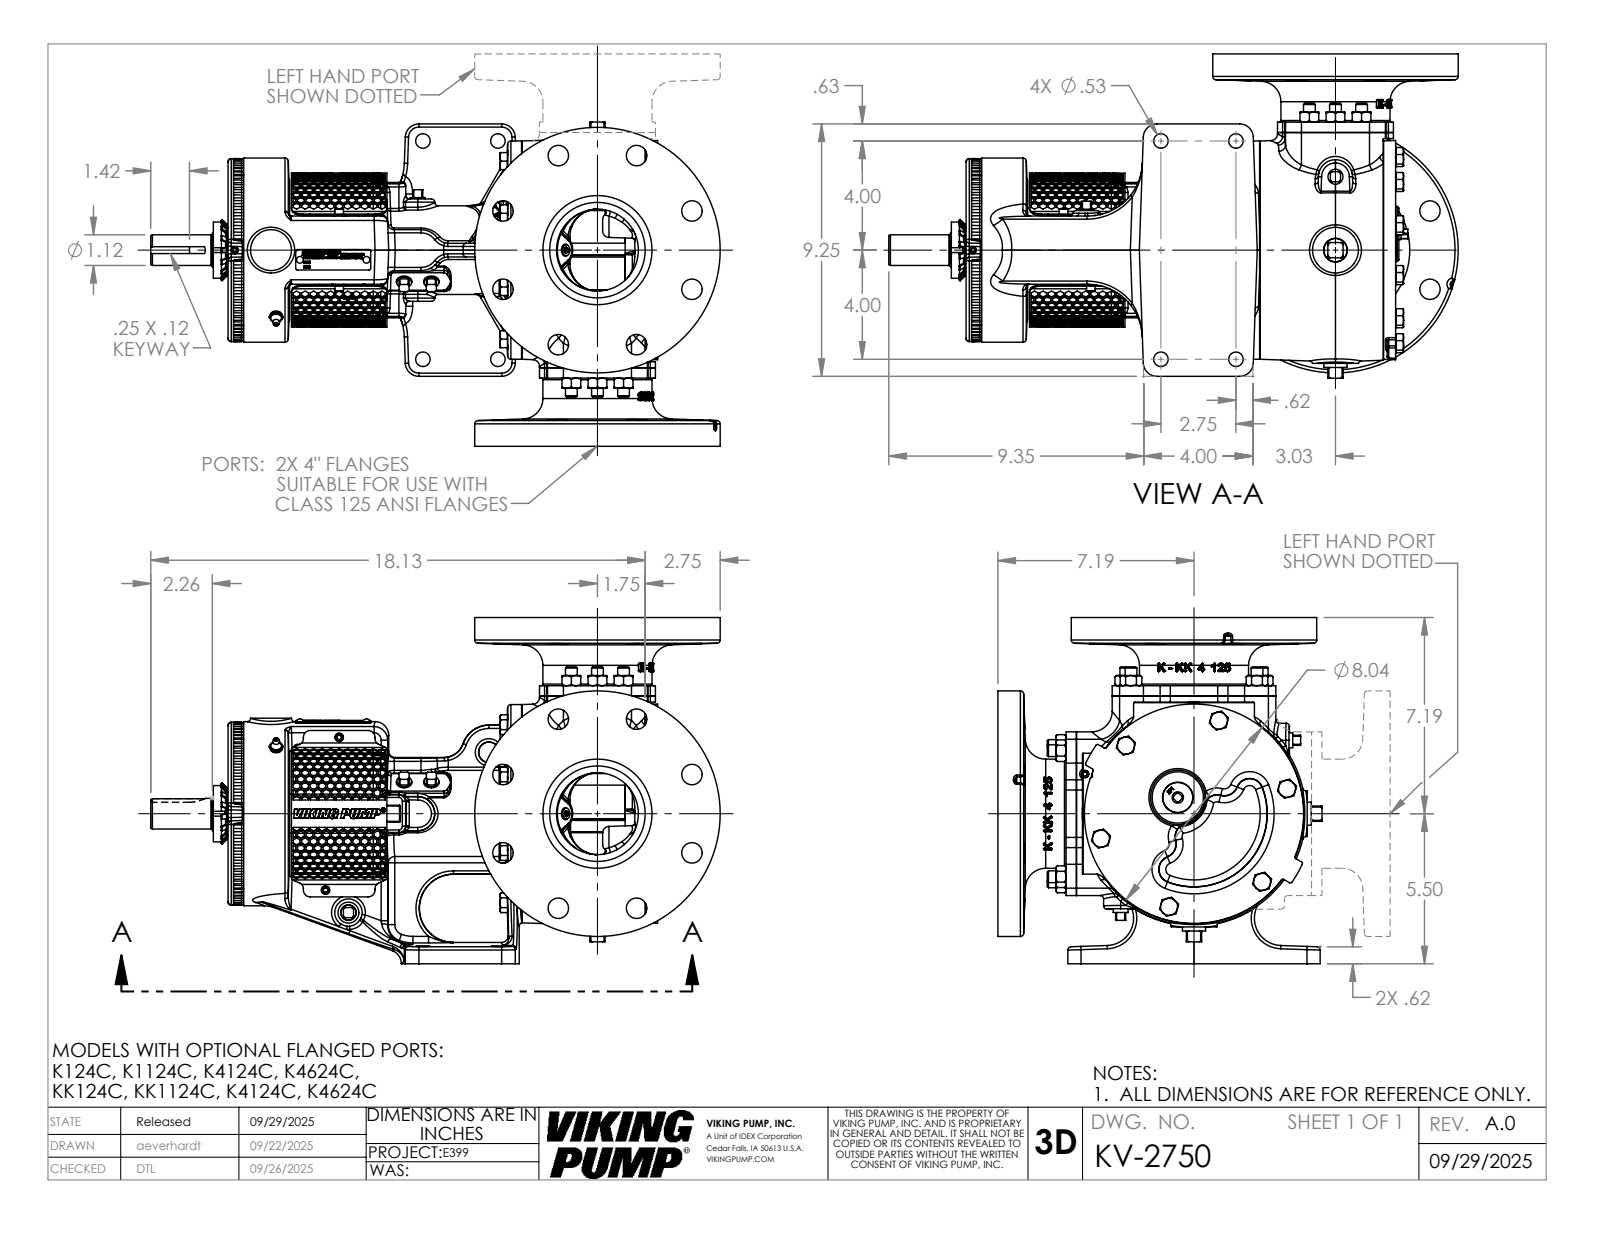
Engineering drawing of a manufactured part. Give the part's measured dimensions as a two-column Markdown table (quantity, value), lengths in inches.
| quantity | value |
| --- | --- |
| part name | KV-2750 |
| STEP written by | SolidWorks 2024 (AUTOMOTIVE_DESIGN) |
| units | inches |
| bodies | 1 solid, 4860 faces (1497 planar, 670 cylindrical, 2693 other) |
| overall size | 20.879 × 12.69 × 11.885 |
| volume | 613.1 in³ |
| surface area | 1 259 in² |
| round holes (diameter × count) | 0.75 × 16, 0.78 × 8, 0.25 × 6, 0.531 × 4, 0.159 × 2, 0.313 × 2, 3 × 2, 0.257 × 1, 0.453 × 1, 1.122 × 1, 1.38 × 1, 1.387 × 1 |
| round bosses / shafts (diameter × count) | 0.431 × 12, 0.625 × 11, 0.625 × 3, 0.437 × 3, 0.312 × 3, 9 × 2, 4 × 2, 8 × 1 |
| partial cylindrical surfaces (radius × count) | 0.12 × 79, 0.01 × 62, 0.03 × 18, 0.24 × 18, 1 × 18, 0.12 × 16, 0.06 × 14, 0.25 × 10 |
| main face-to-face distances | 12.69, 10.425, 2.5, 5.324, 15.749, 2.88, 0.5, 0.574, 4.75, 15.175 |
| hole center spacings | 2.87, 3.75, 5.303, 6.929, 3, 4.994, 5.438, 1.376 |
